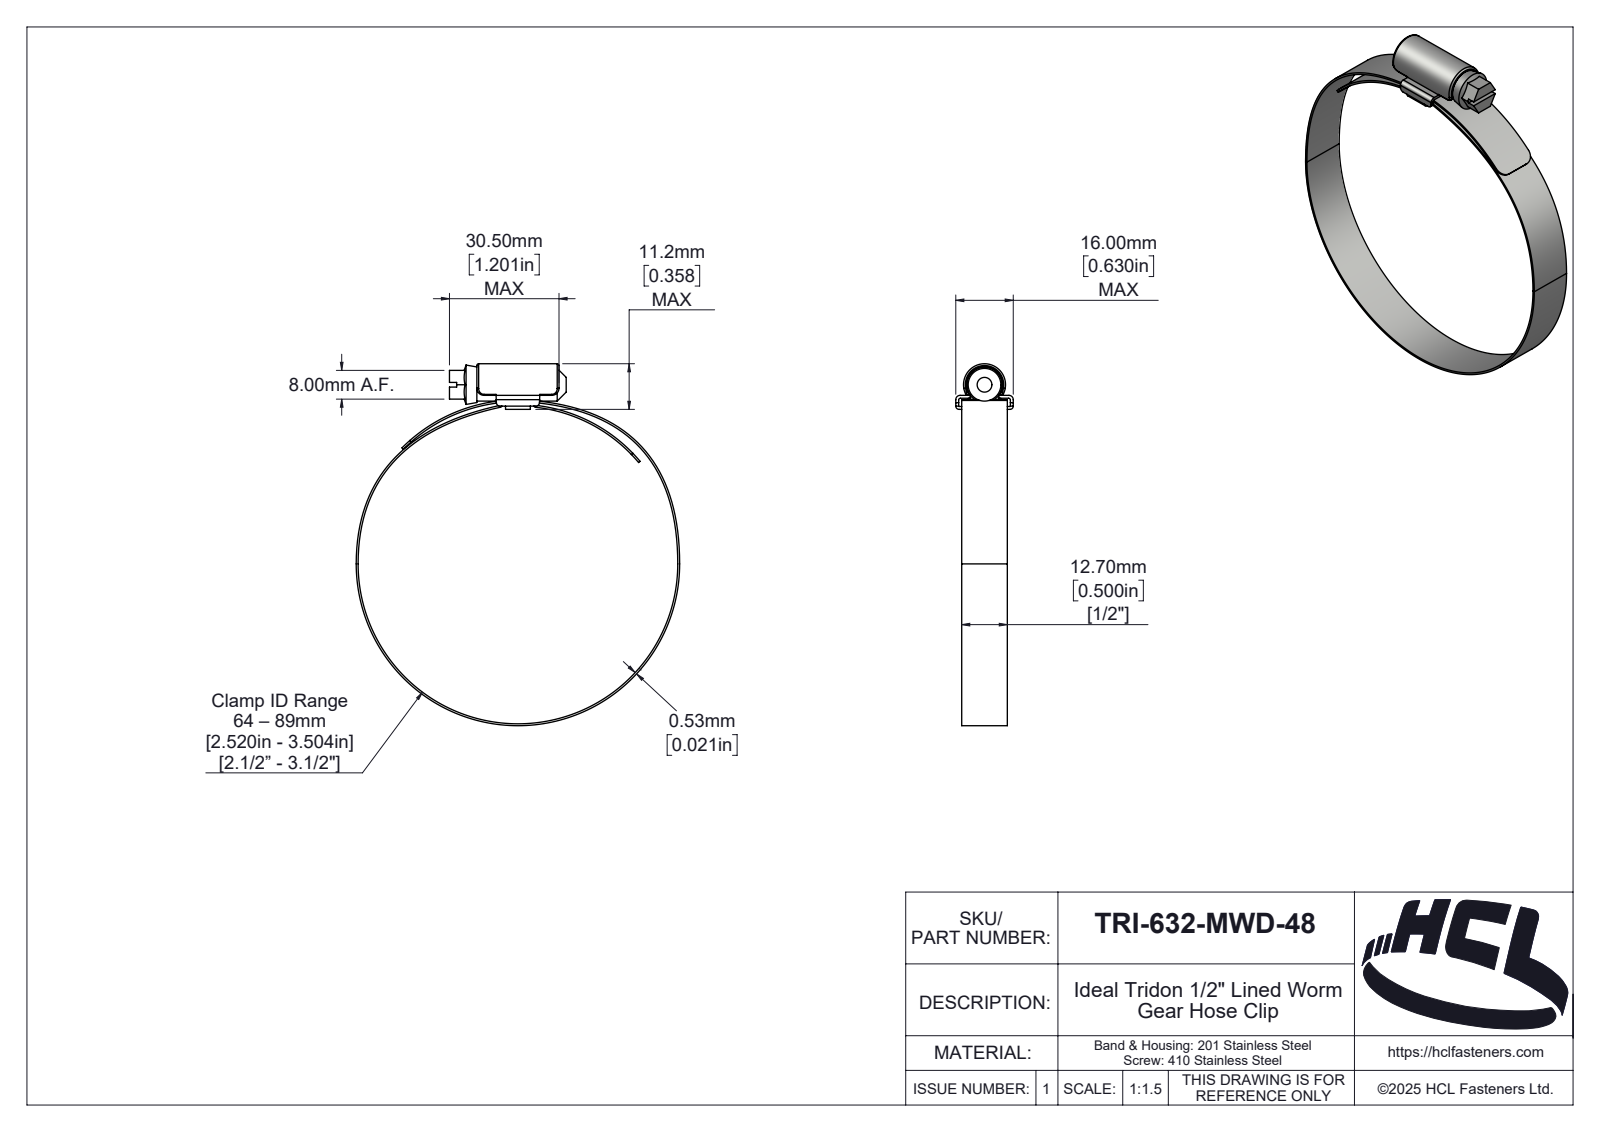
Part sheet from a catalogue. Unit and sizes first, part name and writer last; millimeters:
Units: millimetres
Overall size (bounding box): 100.73 × 90.06 × 16
Round bosses / shafts (diameter × count): ⌀9.1 ×1
Partial cylindrical surfaces — rounded edges, fillets, slot ends (radius × count): R0.5 ×10, R3 ×4, R0.1 ×2, R0.9 ×2, R1 ×2, R1.03 ×2, R1.2 ×2, R2 ×2
Main face-to-face distances: 0.8, 12.7, 3.1, 2.3, 3.9, 1.65, 14.35, 15.2, 0.85, 13.55
Volume: 5 066 mm³ · Surface area: 12 198 mm²
Bodies: 3 solids, 217 faces (49 planar, 99 cylindrical, 69 other)
Part name (STEP PRODUCT): TRI-632-MWD-48
STEP written by: SolidWorks 2025 (AUTOMOTIVE_DESIGN)
